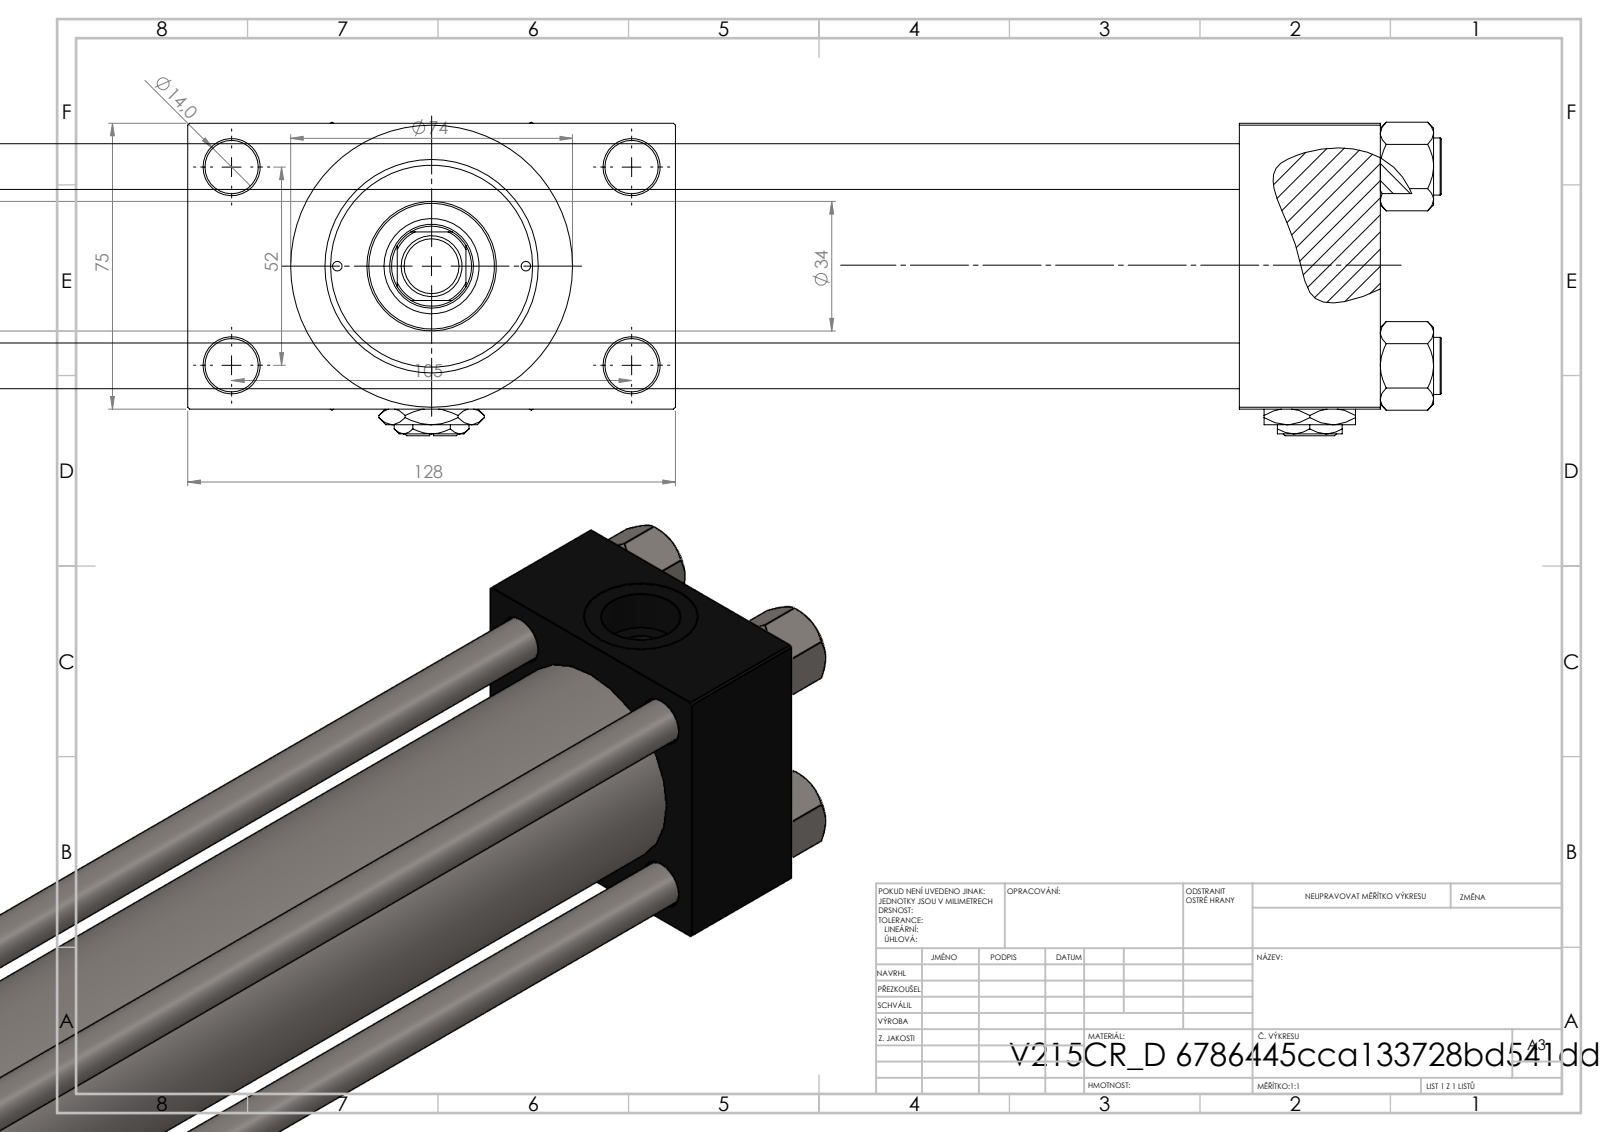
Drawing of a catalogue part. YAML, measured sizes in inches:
part_name: "V215_VC_A; Zatka_pro_OIL_PORT; NUT_M5_D; V215CR_D_Body (+3 more)"
step_written_by: "SolidWorks 2019 (CONFIG_CONTROL_DESIGN)"
units: inches
bodies: {solids: 14, faces: 1227, planar: 551, cylindrical: 108, other: 568}
overall_size: [19.567, 5.039, 3.239]
volume: 71.95
surface_area: 504.5
round_holes:
  - {diameter: 0.472, count: 4}
  - {diameter: 0.551, count: 4}
  - {diameter: 0.098, count: 2}
  - {diameter: 0.276, count: 2}
  - {diameter: 0.825, count: 2}
  - {diameter: 1.181, count: 2}
  - {diameter: 0.413, count: 1}
  - {diameter: 0.866, count: 1}
  - {diameter: 0.984, count: 1}
  - {diameter: 1.614, count: 1}
  - {diameter: 1.969, count: 1}
  - {diameter: 2.087, count: 1}
round_bosses_or_shafts:
  - {diameter: 0.591, count: 4}
  - {diameter: 2.913, count: 1}
  - {diameter: 2.205, count: 1}
  - {diameter: 1.339, count: 1}
  - {diameter: 0.63, count: 1}
  - {diameter: 0.551, count: 1}
partial_cylinders:
  - {radius: 0.413, count: 1}
face_to_face_distances: [2.953, 13.307, 1.457, 14.764, 1.043, 3.996, 16.457, 15, 1.693, 0.63]
hole_center_spacings: [1.031, 1.037, 1.456, 1.497, 2.059, 2.253, 2.3, 2.307]
